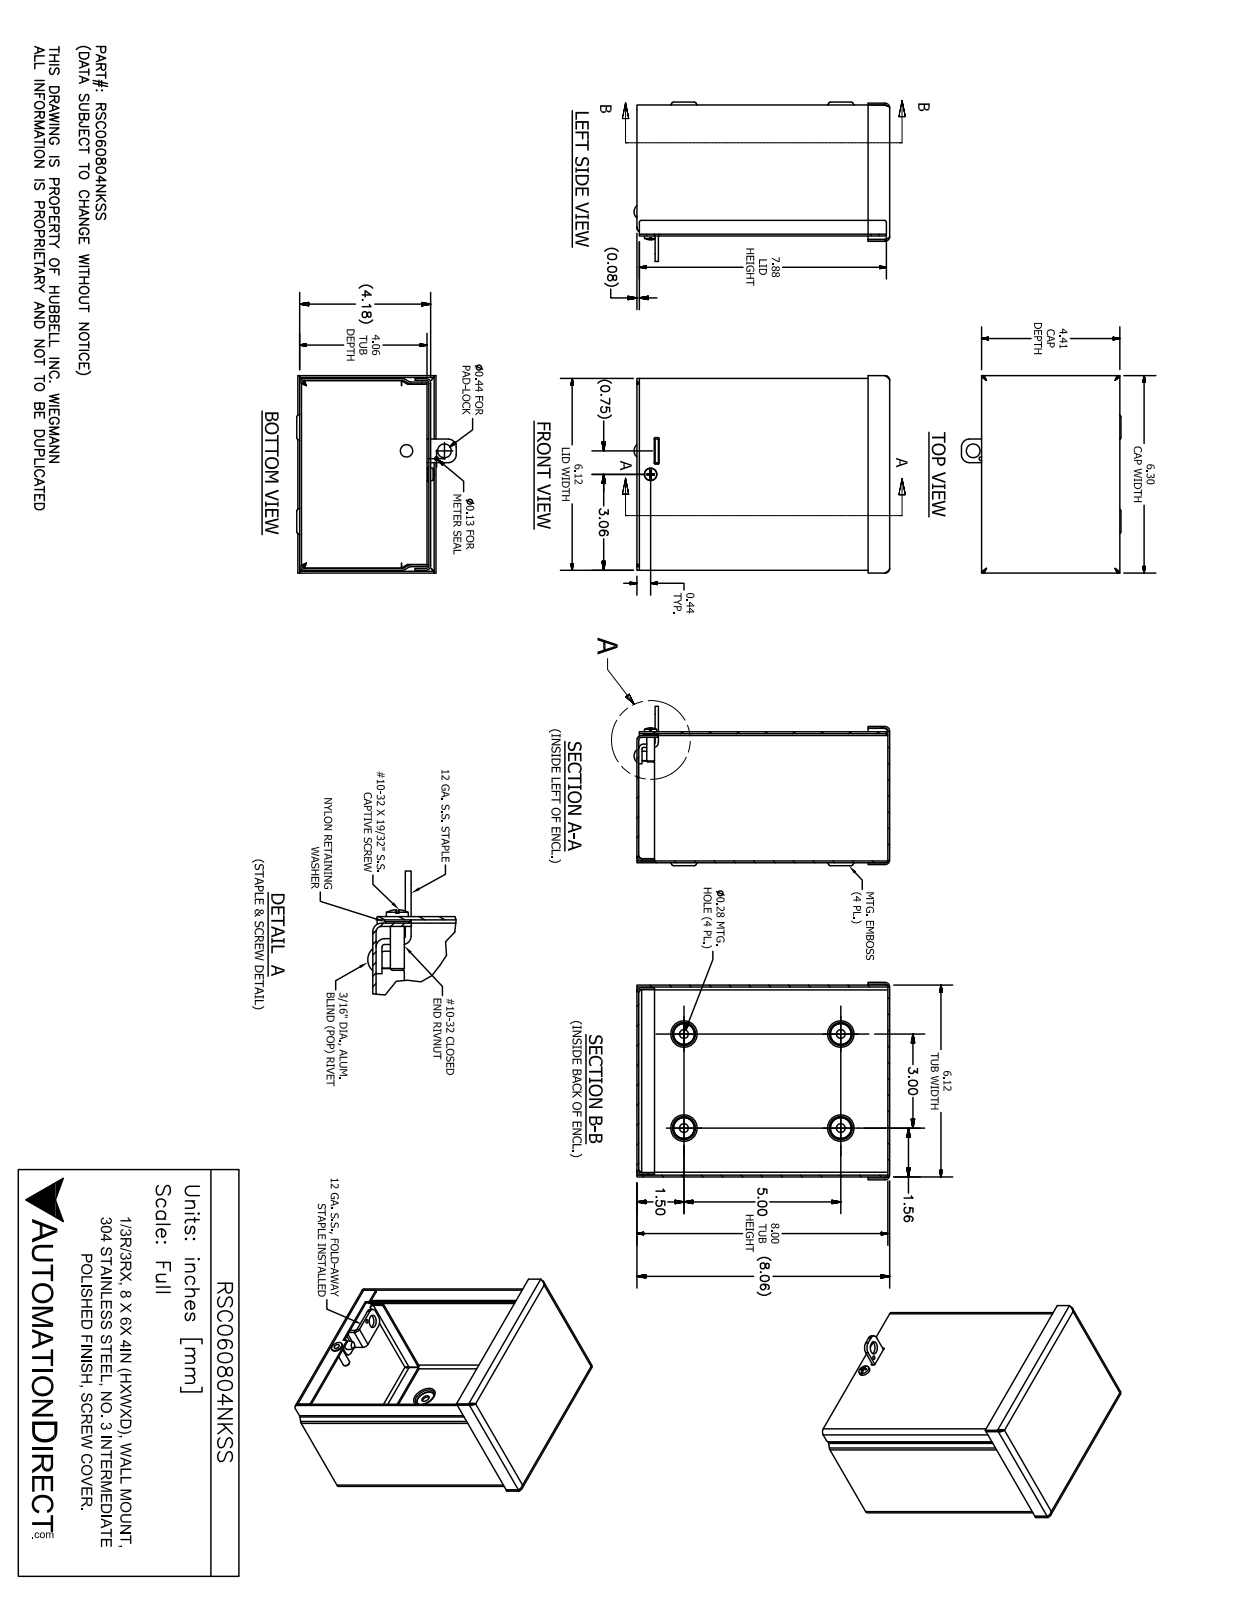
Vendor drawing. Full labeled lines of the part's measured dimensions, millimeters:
Part name (STEP PRODUCT): RSC060804NKSS
STEP written by: SolidWorks 2017 (AUTOMOTIVE_DESIGN)
Units: millimetres
Bodies: 9 solids, 292 faces (149 planar, 79 cylindrical, 64 other)
Overall size (bounding box): 207 × 160 × 129.1
Volume: 234 700 mm³ · Surface area: 317 500 mm²
Round holes (diameter × count): ⌀7.1 ×4, ⌀6.4 ×2, ⌀3.2 ×1, ⌀4 ×1, ⌀5 ×1, ⌀5 ×1, ⌀5.1 ×1, ⌀6.5 ×1, ⌀7.1 ×1, ⌀11.1 ×1
Round bosses / shafts (diameter × count): ⌀11.5 ×1, ⌀10.3 ×1, ⌀6.3 ×1, ⌀4.7 ×1, ⌀4.2 ×1
Partial cylindrical surfaces — rounded edges, fillets, slot ends (radius × count): R2.4 ×16, R3.9 ×16, R0.8 ×6, R6.4 ×4, R1.6 ×3, R1.2 ×2, R1.3 ×2, R3.8 ×2
Main face-to-face distances: 1.5, 104.6, 153.9, 106.1, 103.1, 203.2, 152.4, 155.4, 204.7, 201.7
Hole centre spacings: 46.7, 47.1, 76.2, 127, 148.1, 158.6, 159.4, 9
